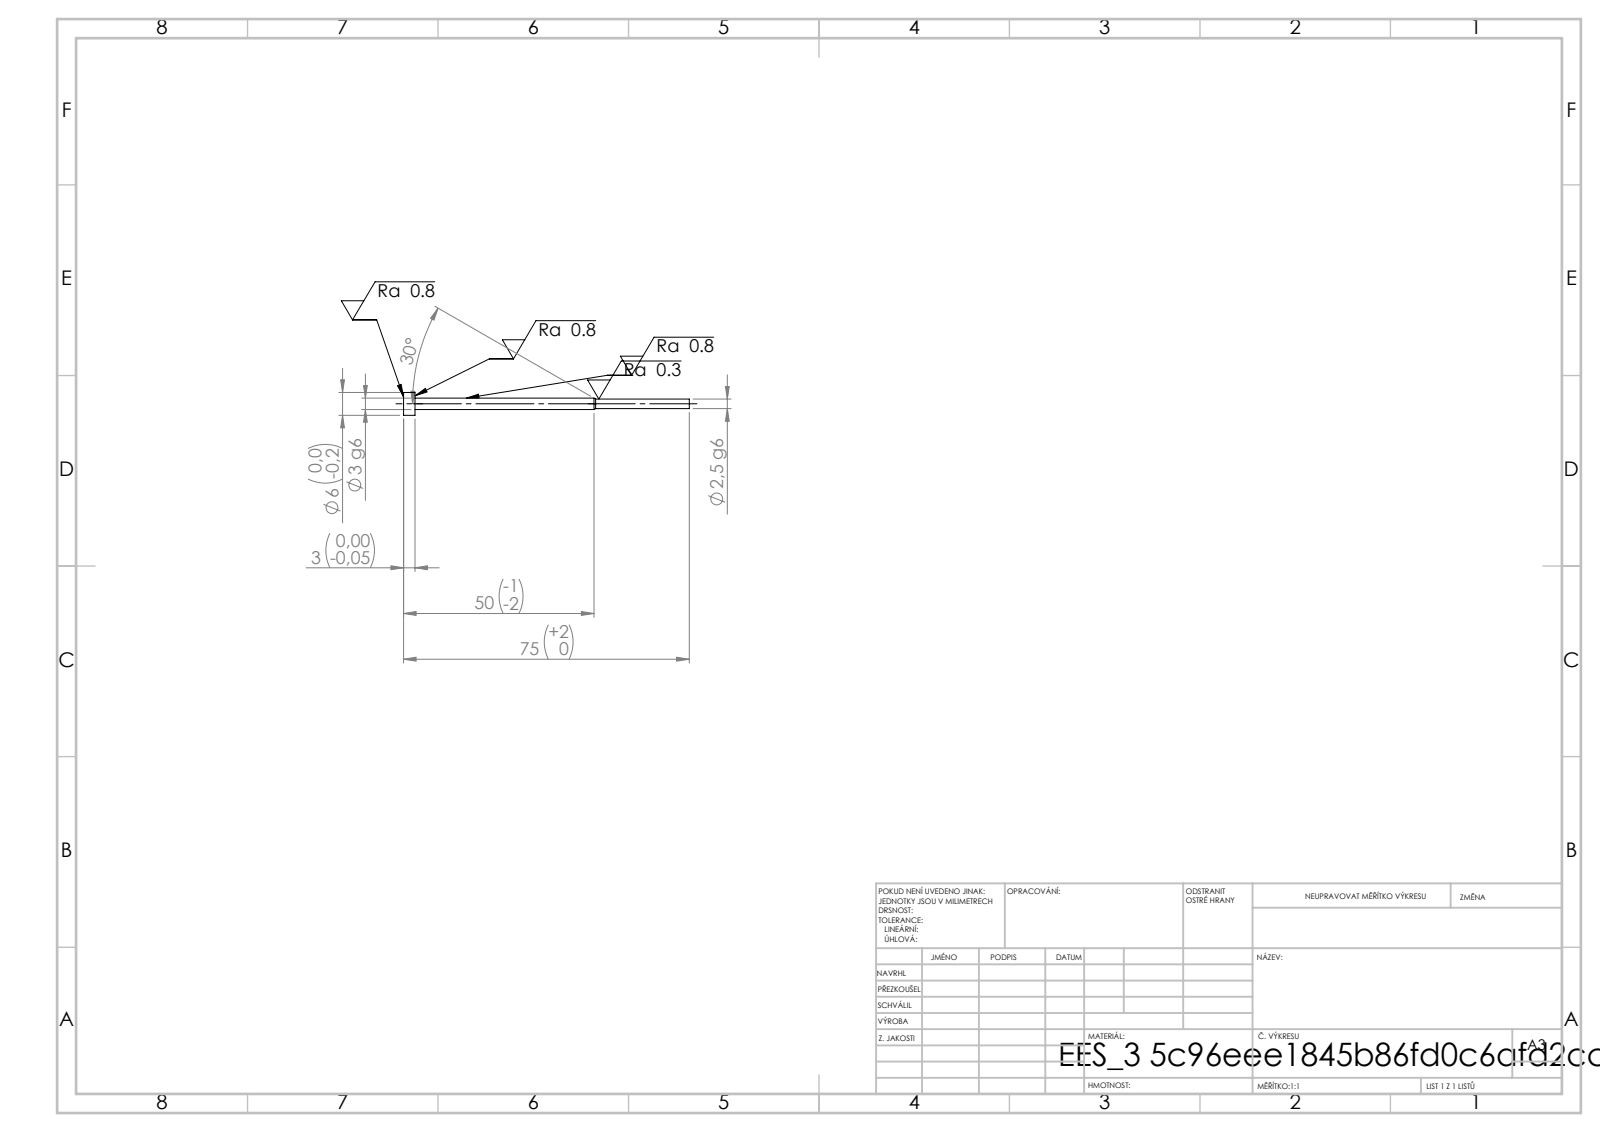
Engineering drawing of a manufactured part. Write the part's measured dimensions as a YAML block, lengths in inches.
step_written_by: "SolidWorks 2019 (CONFIG_CONTROL_DESIGN)"
units: inches
bodies: {solids: 1, faces: 11, planar: 3, cylindrical: 6, other: 2}
overall_size: [2.953, 0.236, 0.236]
volume: 0.033
surface_area: 1.16
round_bosses_or_shafts:
  - {diameter: 0.236, count: 1}
  - {diameter: 0.118, count: 1}
  - {diameter: 0.098, count: 1}
face_to_face_distances: [0.118, 2.835, 2.953]
